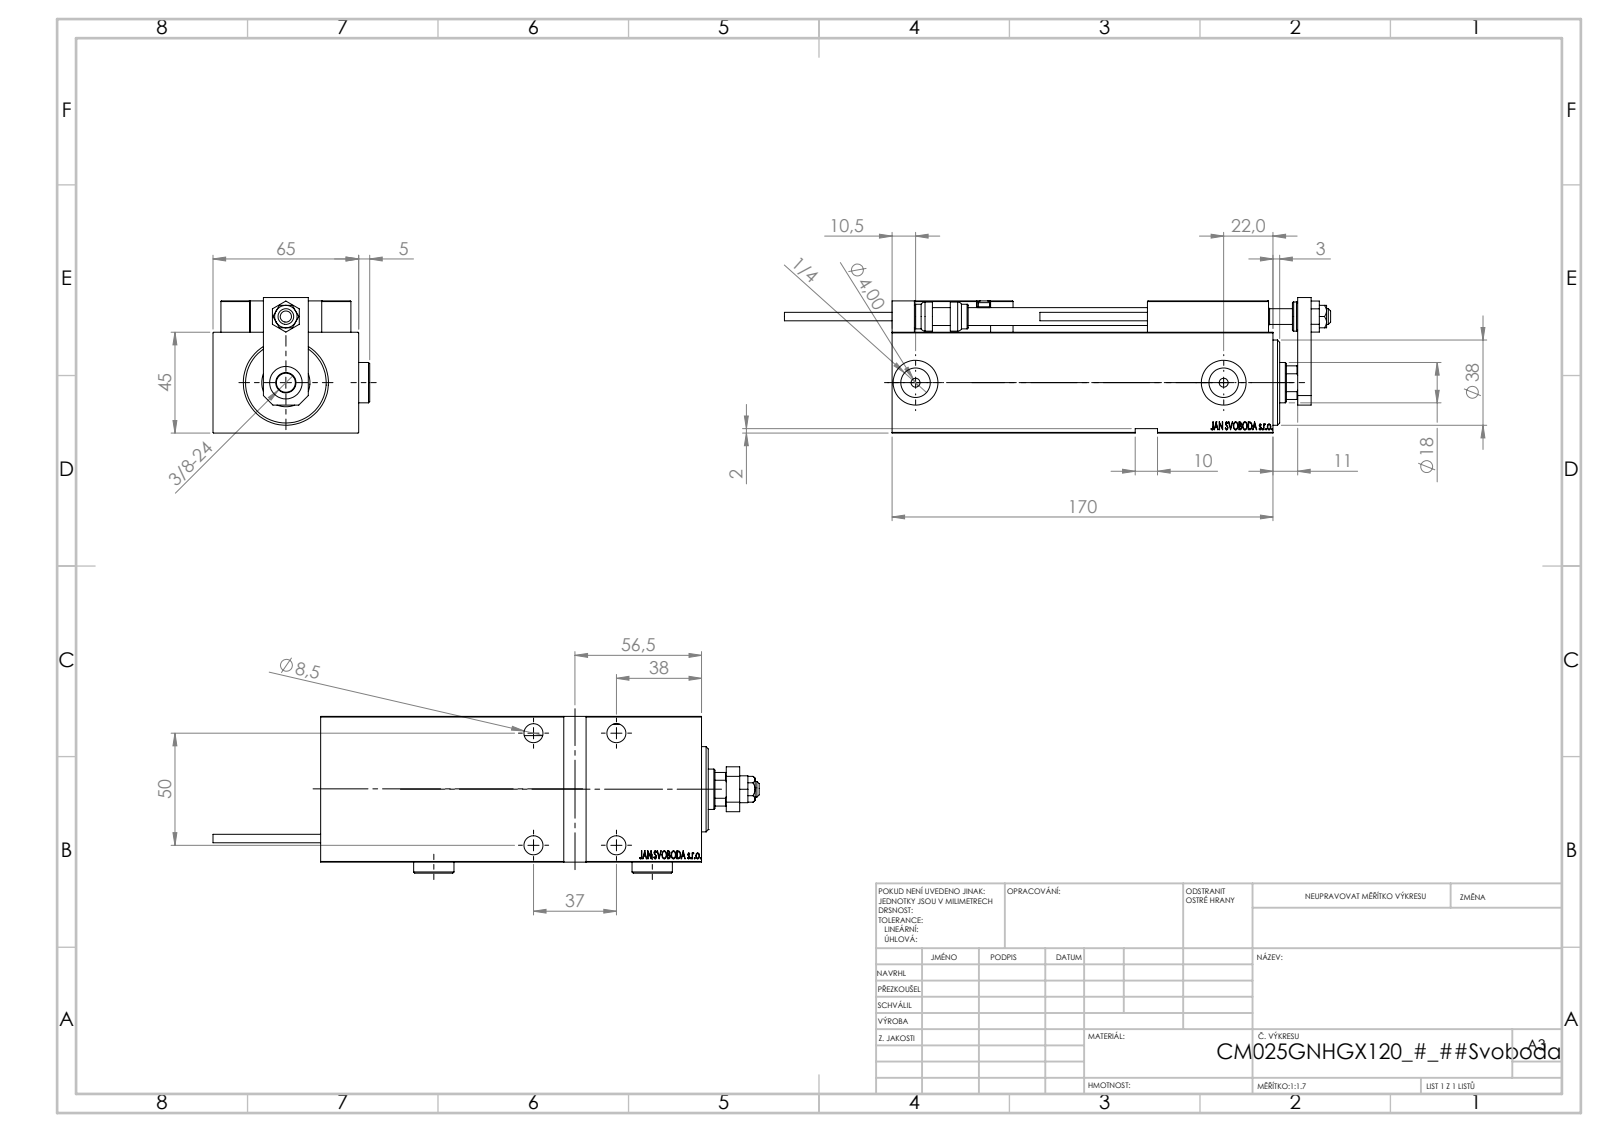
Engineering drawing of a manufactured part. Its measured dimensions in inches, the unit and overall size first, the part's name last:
Units: inches
Overall size (bounding box): 9.594 × 2.752 × 2.382
Round holes (diameter × count): ⌀0.157 ×6, ⌀0.315 ×5, ⌀0.335 ×5, ⌀0.126 ×4, ⌀0.531 ×4, ⌀0.197 ×2, ⌀0.518 ×2, ⌀0.787 ×2, ⌀0.276 ×1, ⌀0.571 ×1, ⌀0.709 ×1, ⌀0.846 ×1
Round bosses / shafts (diameter × count): ⌀0.709 ×2, ⌀0.197 ×2, ⌀0.15 ×2, ⌀1.496 ×1, ⌀0.512 ×1, ⌀0.433 ×1
Partial cylindrical surfaces — rounded edges, fillets, slot ends (radius × count): R0.012 ×30, R0.118 ×2, R0.335 ×1
Main face-to-face distances: 1.772, 2.559, 0.551, 0.236, 2.323, 6.693, 0.512, 7.126, 0.197, 0.748
Hole centre spacings: 0.448, 0.787, 1.165, 1.169, 1.356, 1.42, 1.457, 1.661
Volume: 30.88 in³ · Surface area: 164.6 in²
Bodies: 26 solids, 1334 faces (601 planar, 188 cylindrical, 545 other)
Part name (STEP PRODUCT): Zatka_OIL_PORT; KONCOVKA; NUT_D10; MAGNET (+7 more)
STEP written by: SolidWorks 2019 (CONFIG_CONTROL_DESIGN)
